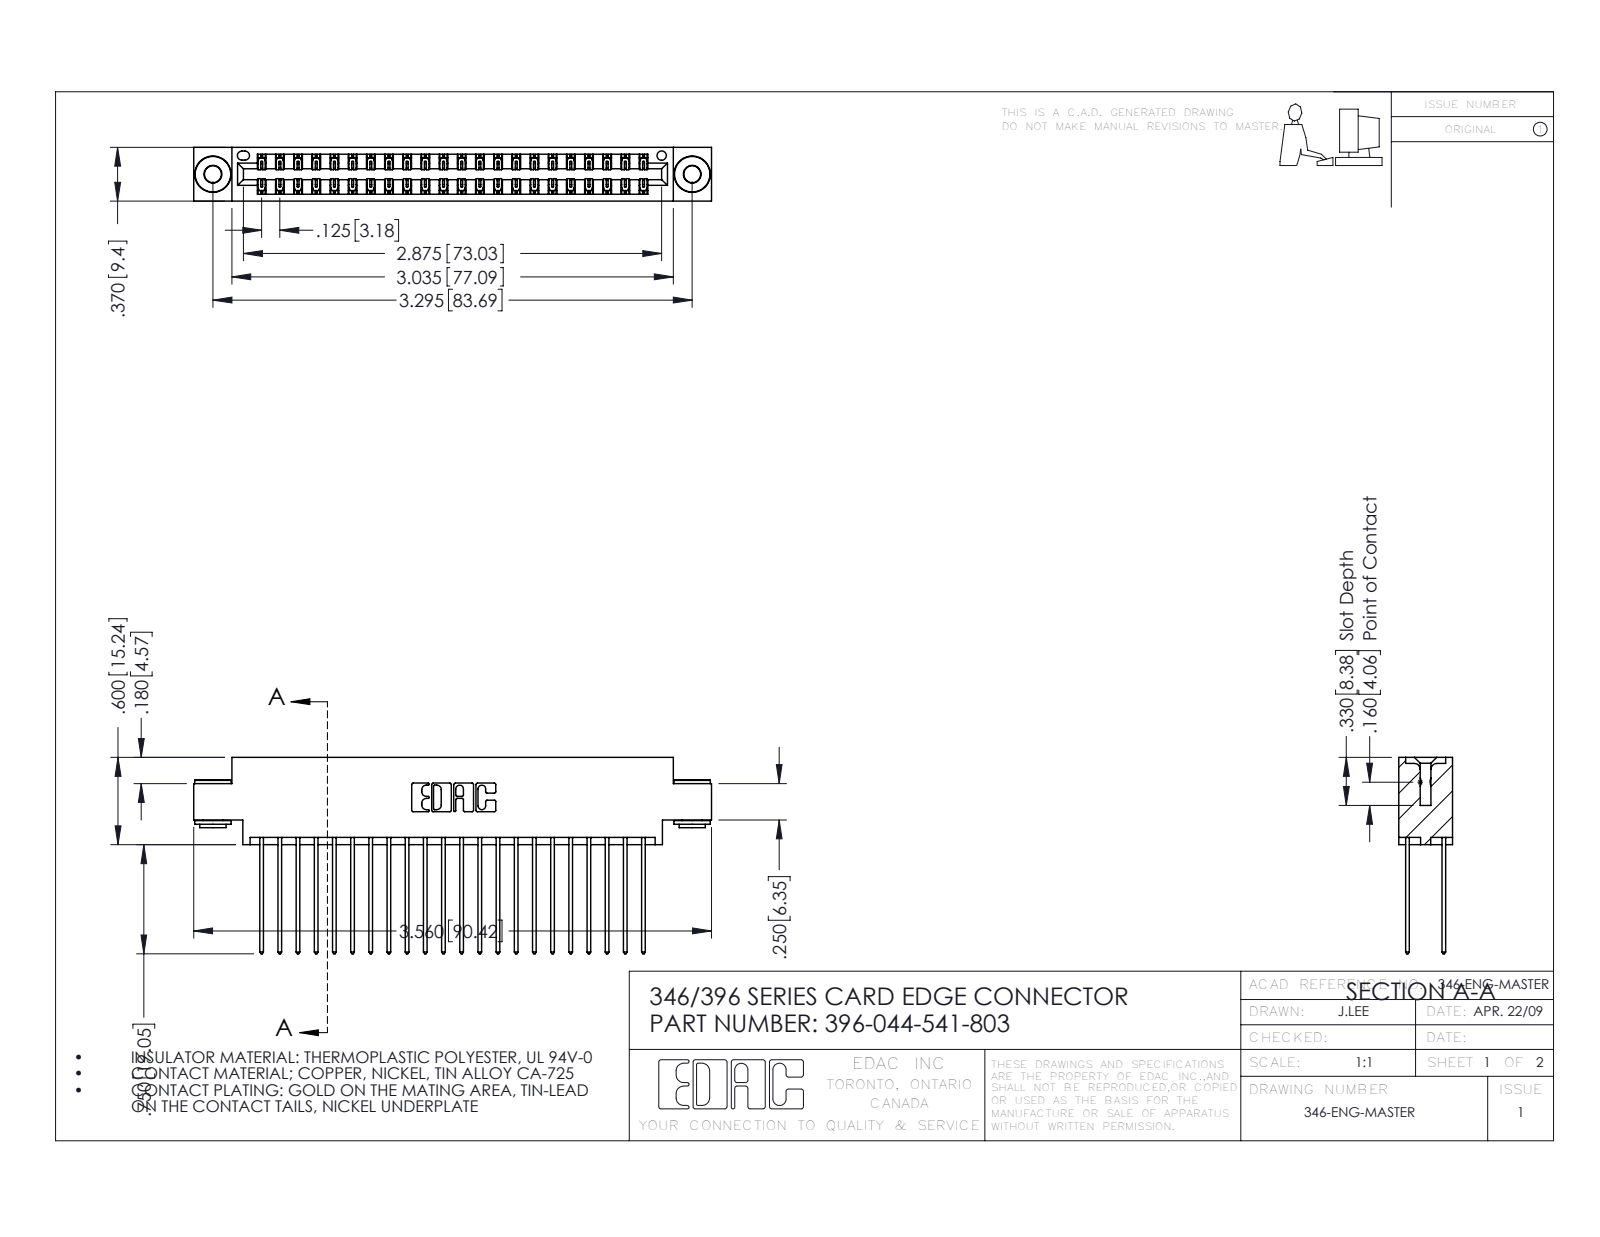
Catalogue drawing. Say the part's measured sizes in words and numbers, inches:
The part is named "345-292-001_345-293-141; 396-044-541-803; 345-250-002_345-250-002-102; 346 Part_0.170 Offset - 0.156 Dia-TH". Its 3-D file was written by "SolidWorks 2016 (CONFIG_CONTROL_DESIGN)". It is 47 solids with 2452 faces: 1630 planar, 814 cylindrical and 8 other. Overall it measures 3.56 by 1.35 by 0.37 inches. Its volume is 0.536 cubic inches and its surface area 20.7 square inches. Round holes: 2 of diameter 0.116, 2 of diameter 0.156, 1 of diameter 0.064. Round bosses or shafts: 2 of diameter 0.25, 2 of diameter 0.18, 2 of diameter 0.136. Partial cylindrical surfaces (rounded edges, fillets, slot ends): 66 of radius 0.006, 44 of radius 0.01, 22 of radius 0.01, 6 of radius 0.007, 6 of radius 0.031, 3 of radius 0.026, 2 of radius 0.014, 2 of radius 0.022. The main face-to-face distances are 0.048, 0.322, 0.25, 0.025, 0.072, 0.298, 0.37, 0.275, 0.225, 0.148. The hole center spacings are 0.246, 3.087, 3.295.
